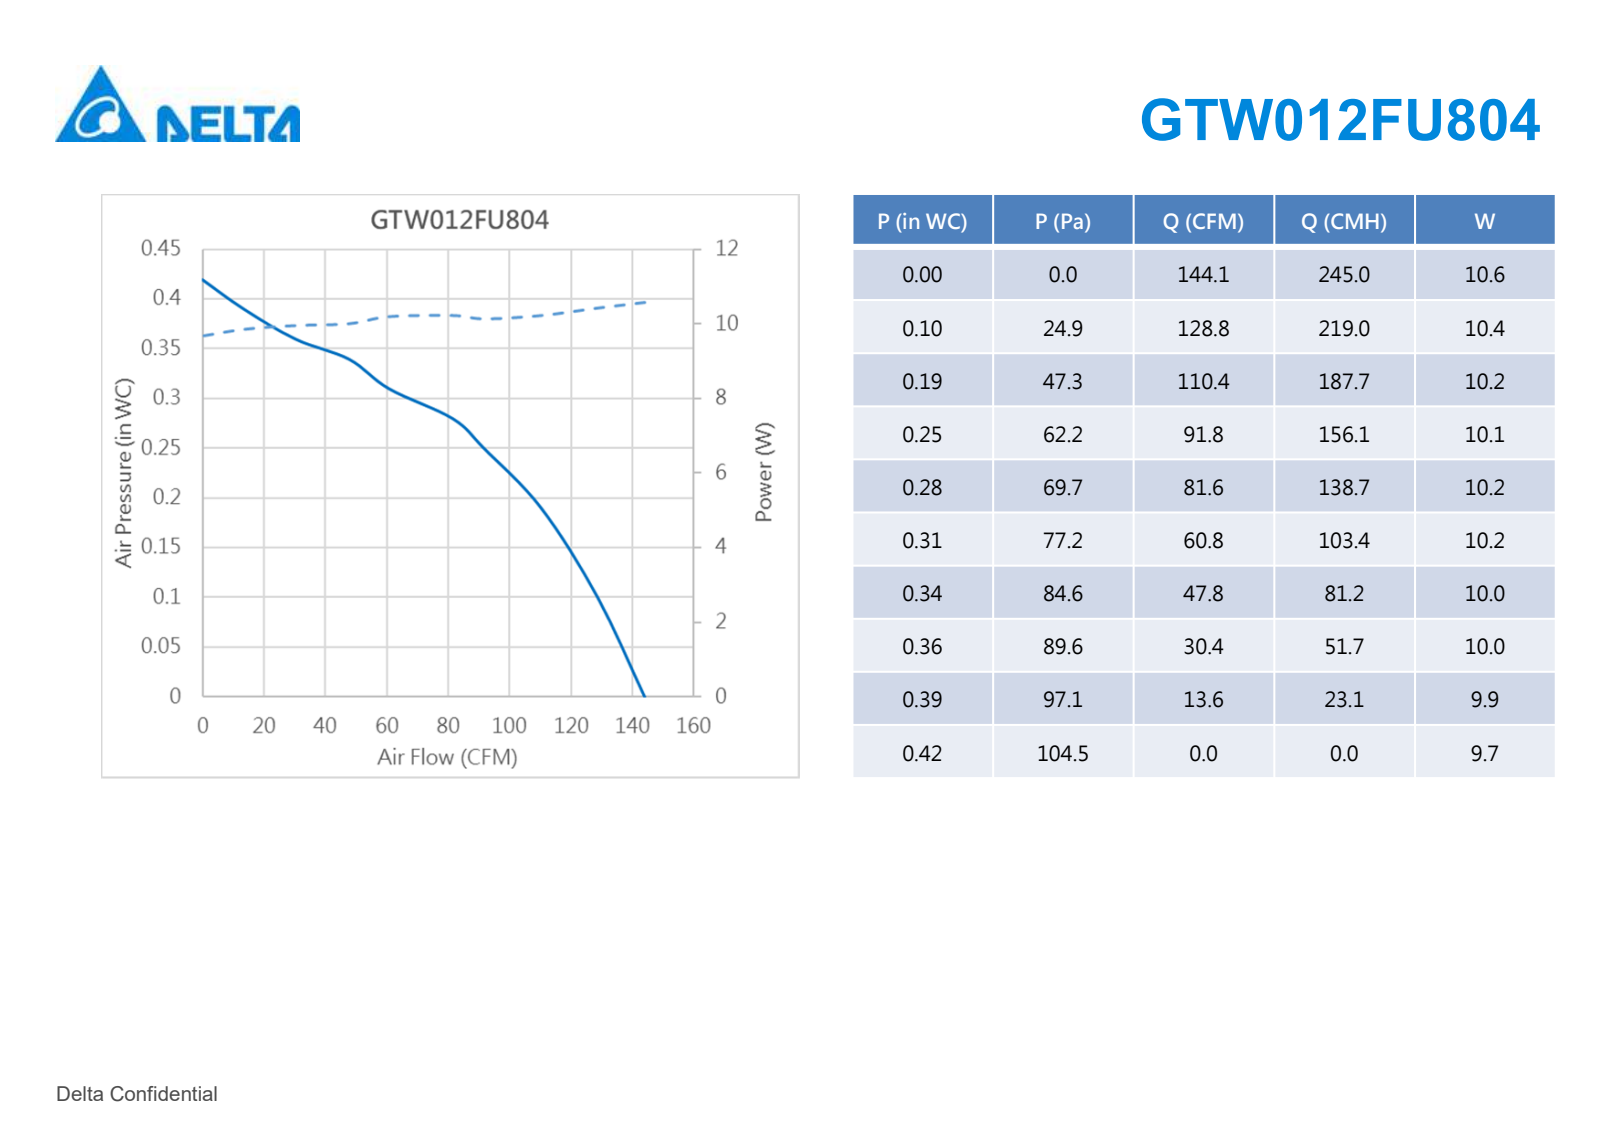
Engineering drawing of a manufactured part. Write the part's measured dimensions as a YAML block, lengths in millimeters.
part_name: "GTW012FU804"
step_written_by: "SolidWorks 2011 (AUTOMOTIVE_DESIGN)"
units: millimeters
bodies: {solids: 3, faces: 2427, planar: 905, cylindrical: 709, other: 813}
overall_size: [120.4, 120.2, 38.7]
volume: 127328
surface_area: 110624
round_holes:
  - {diameter: 4.5, count: 4}
  - {diameter: 2, count: 1}
  - {diameter: 7, count: 1}
  - {diameter: 8, count: 1}
  - {diameter: 9.4, count: 1}
  - {diameter: 14, count: 1}
  - {diameter: 54.8, count: 1}
  - {diameter: 57, count: 1}
  - {diameter: 116, count: 1}
round_bosses_or_shafts:
  - {diameter: 114, count: 1}
  - {diameter: 61, count: 1}
  - {diameter: 14.1, count: 1}
  - {diameter: 13.2, count: 1}
  - {diameter: 12, count: 1}
  - {diameter: 10, count: 1}
  - {diameter: 9.6, count: 1}
partial_cylinders:
  - {radius: 1, count: 109}
  - {radius: 2, count: 54}
  - {radius: 0.5, count: 45}
  - {radius: 0.3, count: 12}
  - {radius: 0.2, count: 10}
  - {radius: 2.92, count: 9}
  - {radius: 21.54, count: 9}
  - {radius: 0.8, count: 8}
face_to_face_distances: [2, 7.5, 2.5, 120, 27, 33, 16.5, 19.5, 5, 11]
hole_center_spacings: [74.25, 105, 148.49]
